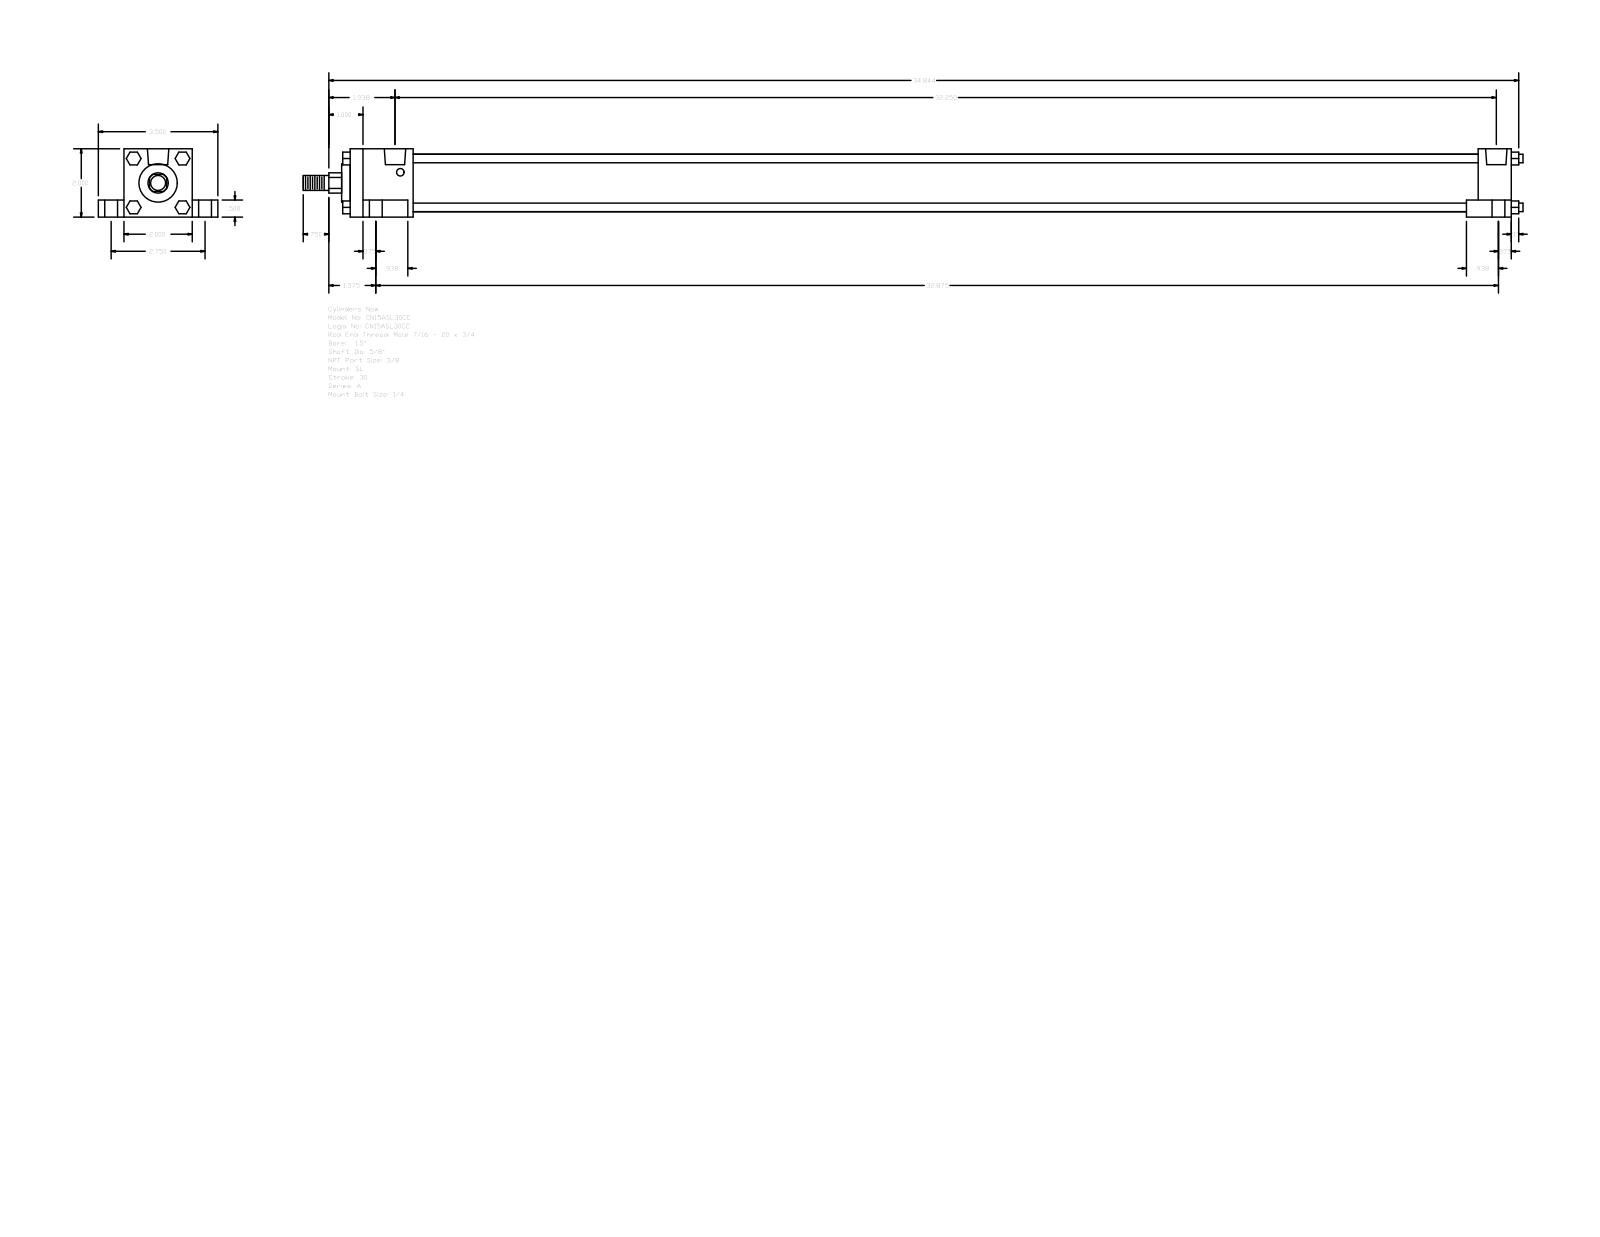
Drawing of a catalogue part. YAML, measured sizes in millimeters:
part_name: "A_SL__0150_0.625"
step_written_by: "GSSL Pune (CONFIG_CONTROL_DESIGN)"
units: millimeters
bodies: {solids: 0, faces: 148, planar: 112, cylindrical: 36, other: 0}
overall_size: [907.26, 88.9, 50.8]
round_holes:
  - {diameter: 5.56, count: 4}
  - {diameter: 9.53, count: 4}
  - {diameter: 15.88, count: 4}
  - {diameter: 15.93, count: 2}
round_bosses_or_shafts:
  - {diameter: 6.35, count: 4}
  - {diameter: 42.93, count: 1}
  - {diameter: 28.57, count: 1}
  - {diameter: 15.88, count: 1}
  - {diameter: 11.11, count: 1}
partial_cylinders:
  - {radius: 7.54, count: 1}
face_to_face_distances: [50.8, 19.05, 38.1, 12.7, 69.85, 863.6, 9.52, 33.34, 838.99, 24.61]
hole_center_spacings: [3.97, 34.96, 35.36, 37.73, 39.41, 69.84, 811.21, 815.18]
